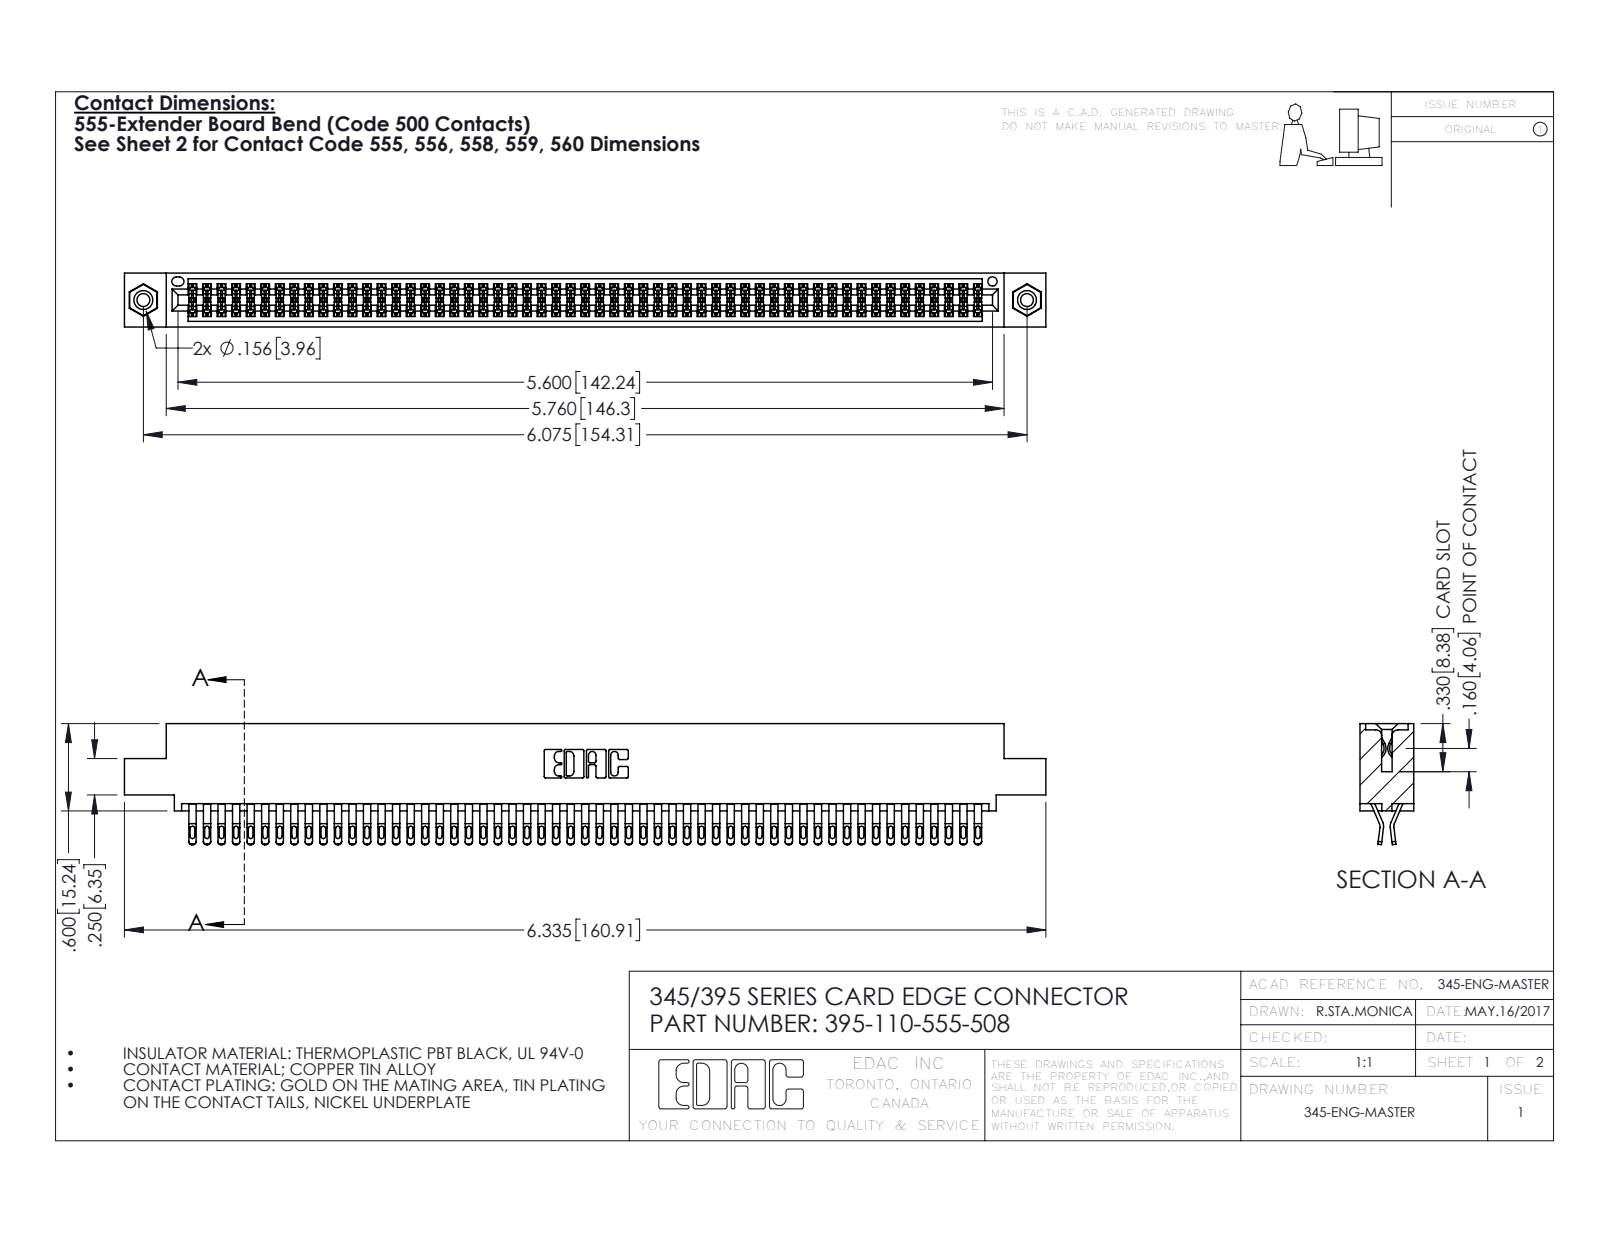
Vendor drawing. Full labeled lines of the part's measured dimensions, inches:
Part name (STEP PRODUCT): 345-250-001_345-250-003-102; 345-292-001_555 Tail; 345 Part_0.110 Offset - 0.156 Dia-TI; 395-110-555-508
STEP written by: SolidWorks 2016 (CONFIG_CONTROL_DESIGN)
Units: inches
Bodies: 113 solids, 6350 faces (3526 planar, 2808 cylindrical, 16 other)
Overall size (bounding box): 6.335 × 0.832 × 0.37
Volume: 0.976 in³ · Surface area: 38.91 in²
Round holes (diameter × count): ⌀0.089 ×2, ⌀0.125 ×2, ⌀0.156 ×2, ⌀0.064 ×1
Round bosses / shafts (diameter × count): ⌀0.155 ×2
Partial cylindrical surfaces — rounded edges, fillets, slot ends (radius × count): R0.016 ×275, R0.02 ×220, R0.006 ×165, R0.01 ×22, R0.007 ×6, R0.031 ×6, R0.026 ×3, R0.01 ×2
Main face-to-face distances: 0.072, 0.298, 0.025, 0.37, 0.2, 0.098, 0.272, 0.225, 0.175, 0.149
Hole centre spacings: 0.27, 5.839, 6.075
